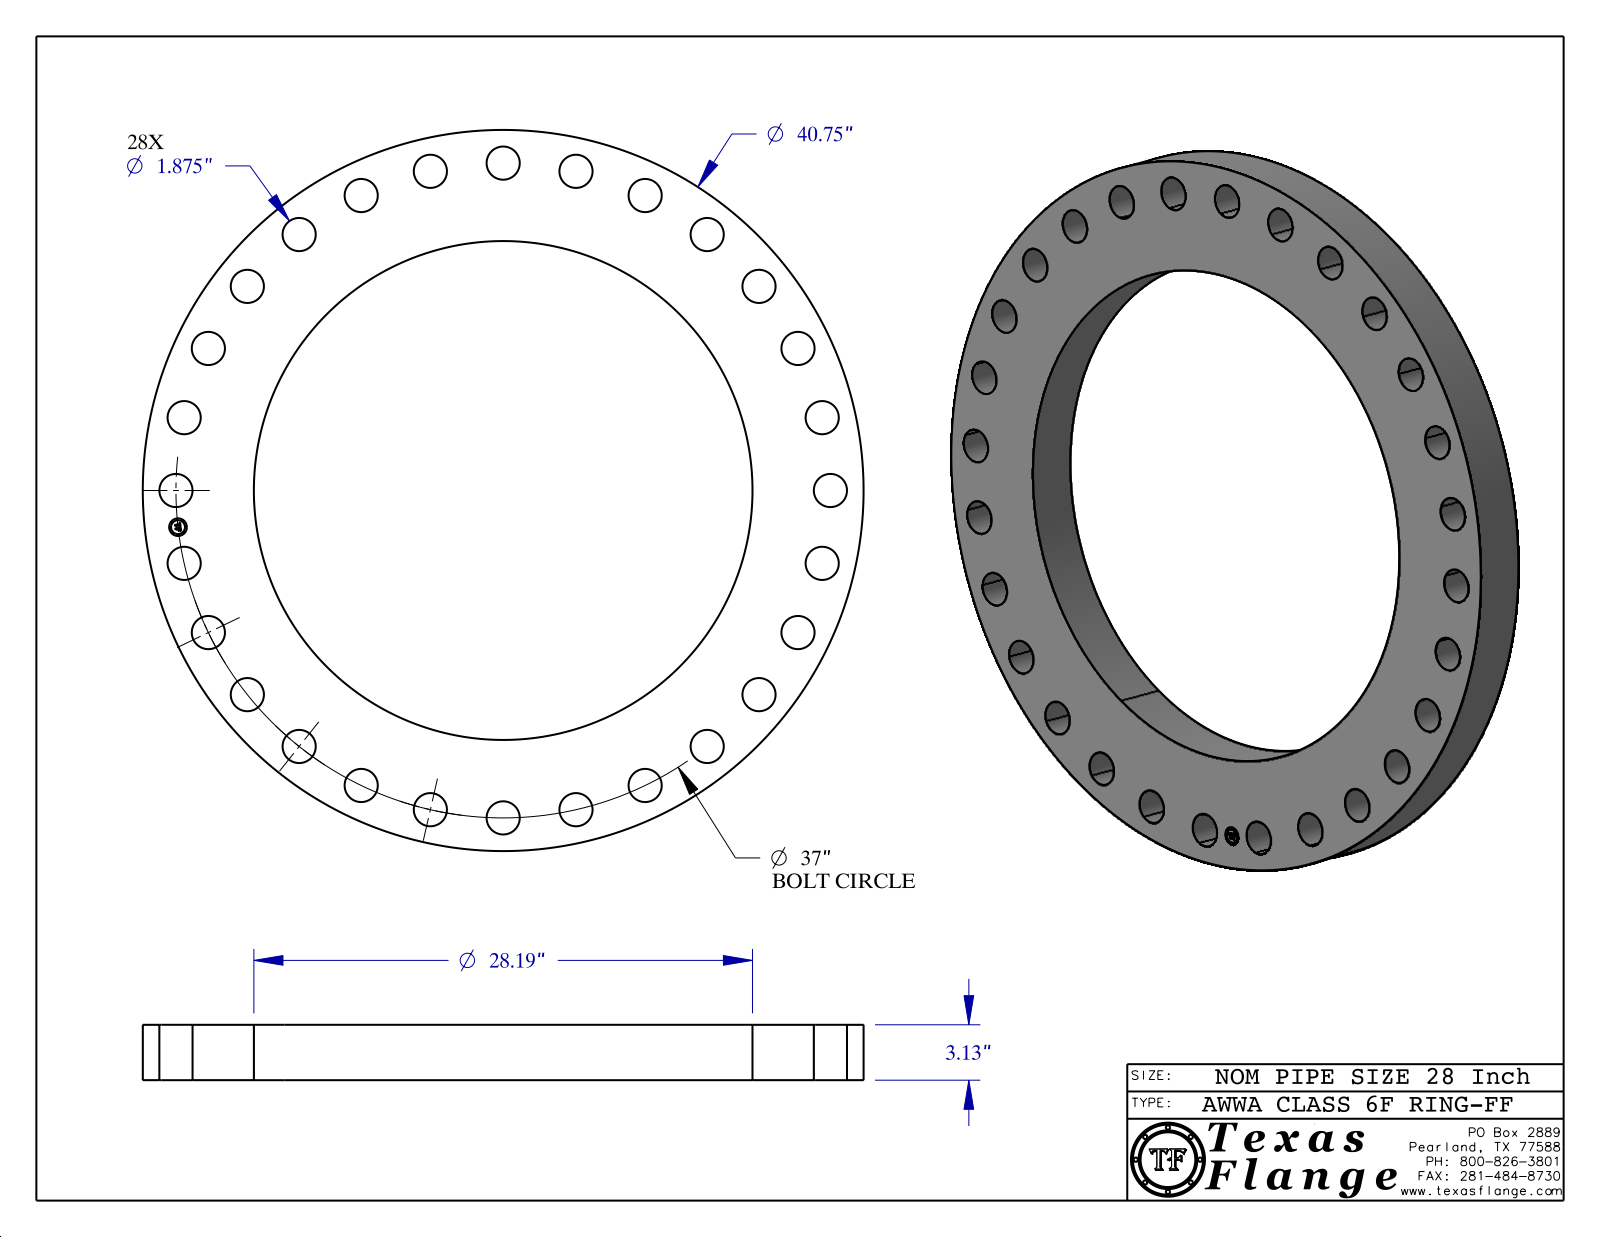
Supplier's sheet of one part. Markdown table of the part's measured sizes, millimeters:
| quantity | value |
| --- | --- |
| part name | AWWA Class 6F-RING-FF |
| STEP written by | CATIA V5 STEP AP214 (AUTOMOTIVE_DESIGN) |
| units | millimeters |
| bodies | 1 solid, 447 faces (367 planar, 80 cylindrical, 0 other) |
| overall size | 1035.1 × 1035.1 × 79.5 |
| volume | 30 920 000 mm³ |
| surface area | 1 548 000 mm² |
| round holes (diameter × count) | 47.6 × 28, 25.4 × 1, 716 × 1 |
| round bosses / shafts (diameter × count) | 1.5 × 8, 1035.1 × 1, 20 × 1 |
| main face-to-face distances | 79.5, 0.4, 79.1, 7.6, 7.4, 1.4, 4.9, 6.3, 1.1, 3.8 |
| hole center spacings | 469.9, 664.5, 795.8, 916.2, 933.9, 846.7, 105.2, 407.8 |
